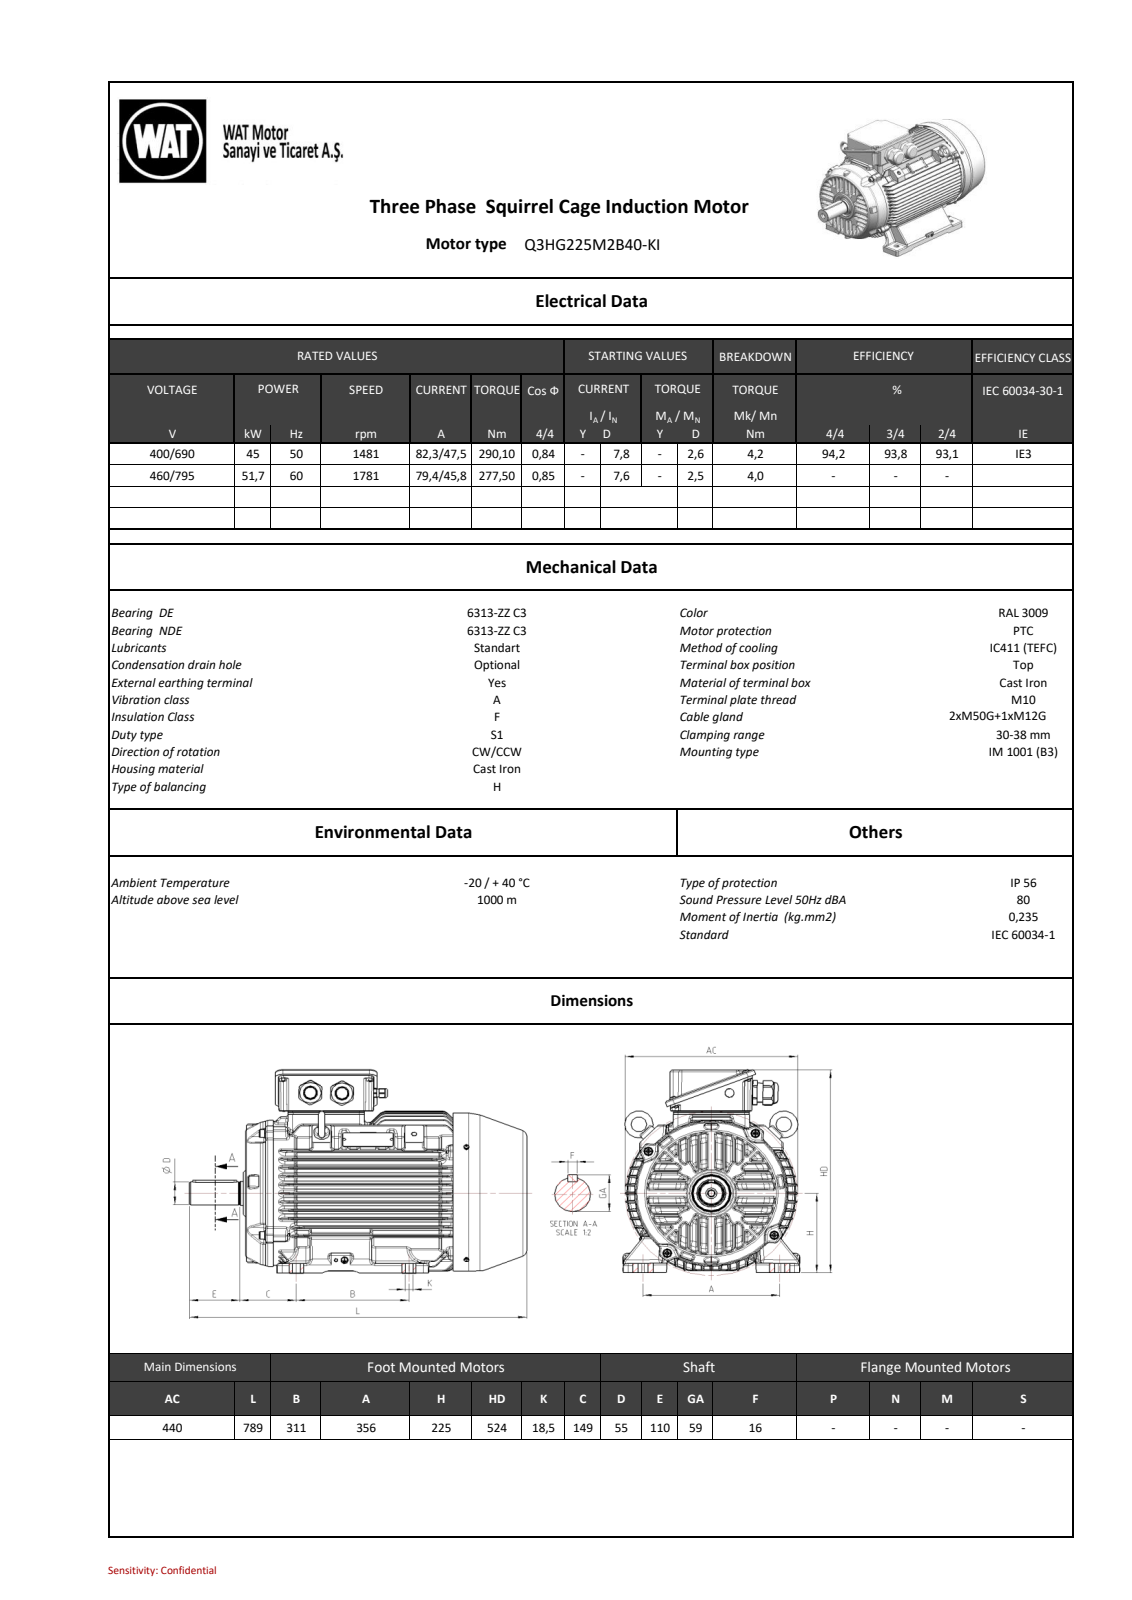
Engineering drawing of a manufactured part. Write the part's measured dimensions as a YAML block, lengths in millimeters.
part_name: "26000A30F4D8rnwh"
step_written_by: "SIEMENS PLM Software NX 11.0 (AUTOMOTIVE_DESIGN)"
units: millimeters
bodies: {solids: 0, faces: 8455, planar: 2842, cylindrical: 1598, other: 4015}
overall_size: [788.12, 523.73, 443]
round_holes:
  - {diameter: 14, count: 10}
  - {diameter: 2.5, count: 1}
  - {diameter: 6.8, count: 1}
  - {diameter: 10, count: 1}
  - {diameter: 17.5, count: 1}
  - {diameter: 21, count: 1}
  - {diameter: 88.33, count: 1}
  - {diameter: 437, count: 1}
round_bosses_or_shafts:
  - {diameter: 24, count: 8}
  - {diameter: 30, count: 4}
  - {diameter: 8, count: 4}
  - {diameter: 35, count: 3}
  - {diameter: 58, count: 2}
  - {diameter: 54.8, count: 2}
  - {diameter: 12, count: 2}
  - {diameter: 440, count: 1}
partial_cylinders:
  - {radius: 4, count: 324}
  - {radius: 2, count: 274}
  - {radius: 3, count: 135}
  - {radius: 5, count: 131}
  - {radius: 6, count: 68}
  - {radius: 0.6, count: 41}
  - {radius: 10, count: 20}
  - {radius: 9.25, count: 12}
face_to_face_distances: [17.41, 159.69, 17.32, 194.42, 34.89, 142.21, 17.48, 88.37, 52.44, 35.03]
hole_center_spacings: [198, 280.01, 68.76, 227.14, 324.38, 389.98, 396, 127.5]
